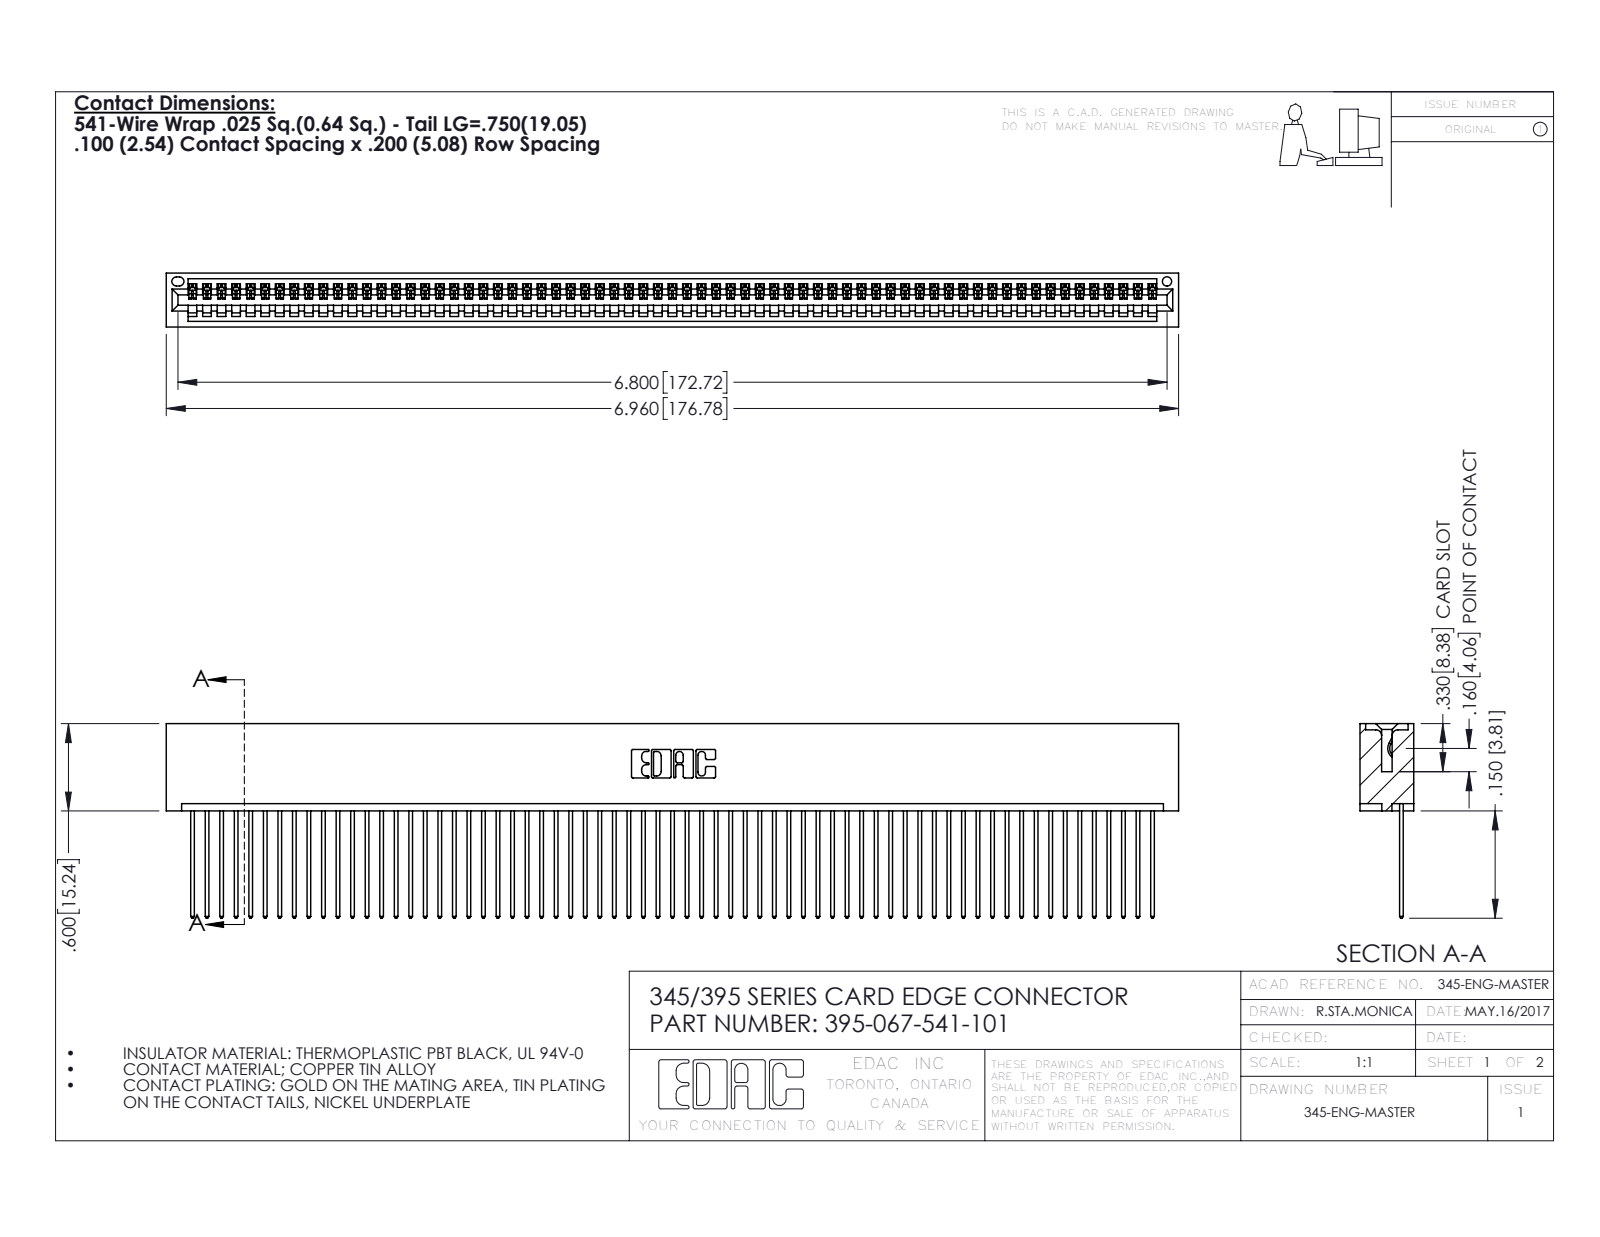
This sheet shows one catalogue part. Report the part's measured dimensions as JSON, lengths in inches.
{"part_name": "395-067-541-101; 345-292-001_345-293-141; 345 Part_No Mounting Lugs", "step_written_by": "SolidWorks 2016 (CONFIG_CONTROL_DESIGN)", "units": "inches", "bodies": {"solids": 68, "faces": 4004, "planar": 2756, "cylindrical": 1248, "other": 0}, "overall_size": [6.96, 1.337, 0.37], "volume_in3": 1.086, "surface_area_in2": 39.51, "round_holes": [[0.064, 1]], "partial_cylinders_radius": [[0.006, 134], [0.01, 134], [0.01, 22], [0.007, 6], [0.031, 6], [0.026, 3], [0.031, 2], [0.04, 2]], "face_to_face_distances": [0.072, 0.298, 0.098, 0.272, 0.025, 0.37, 0.2, 0.225, 0.149, 0.072]}
